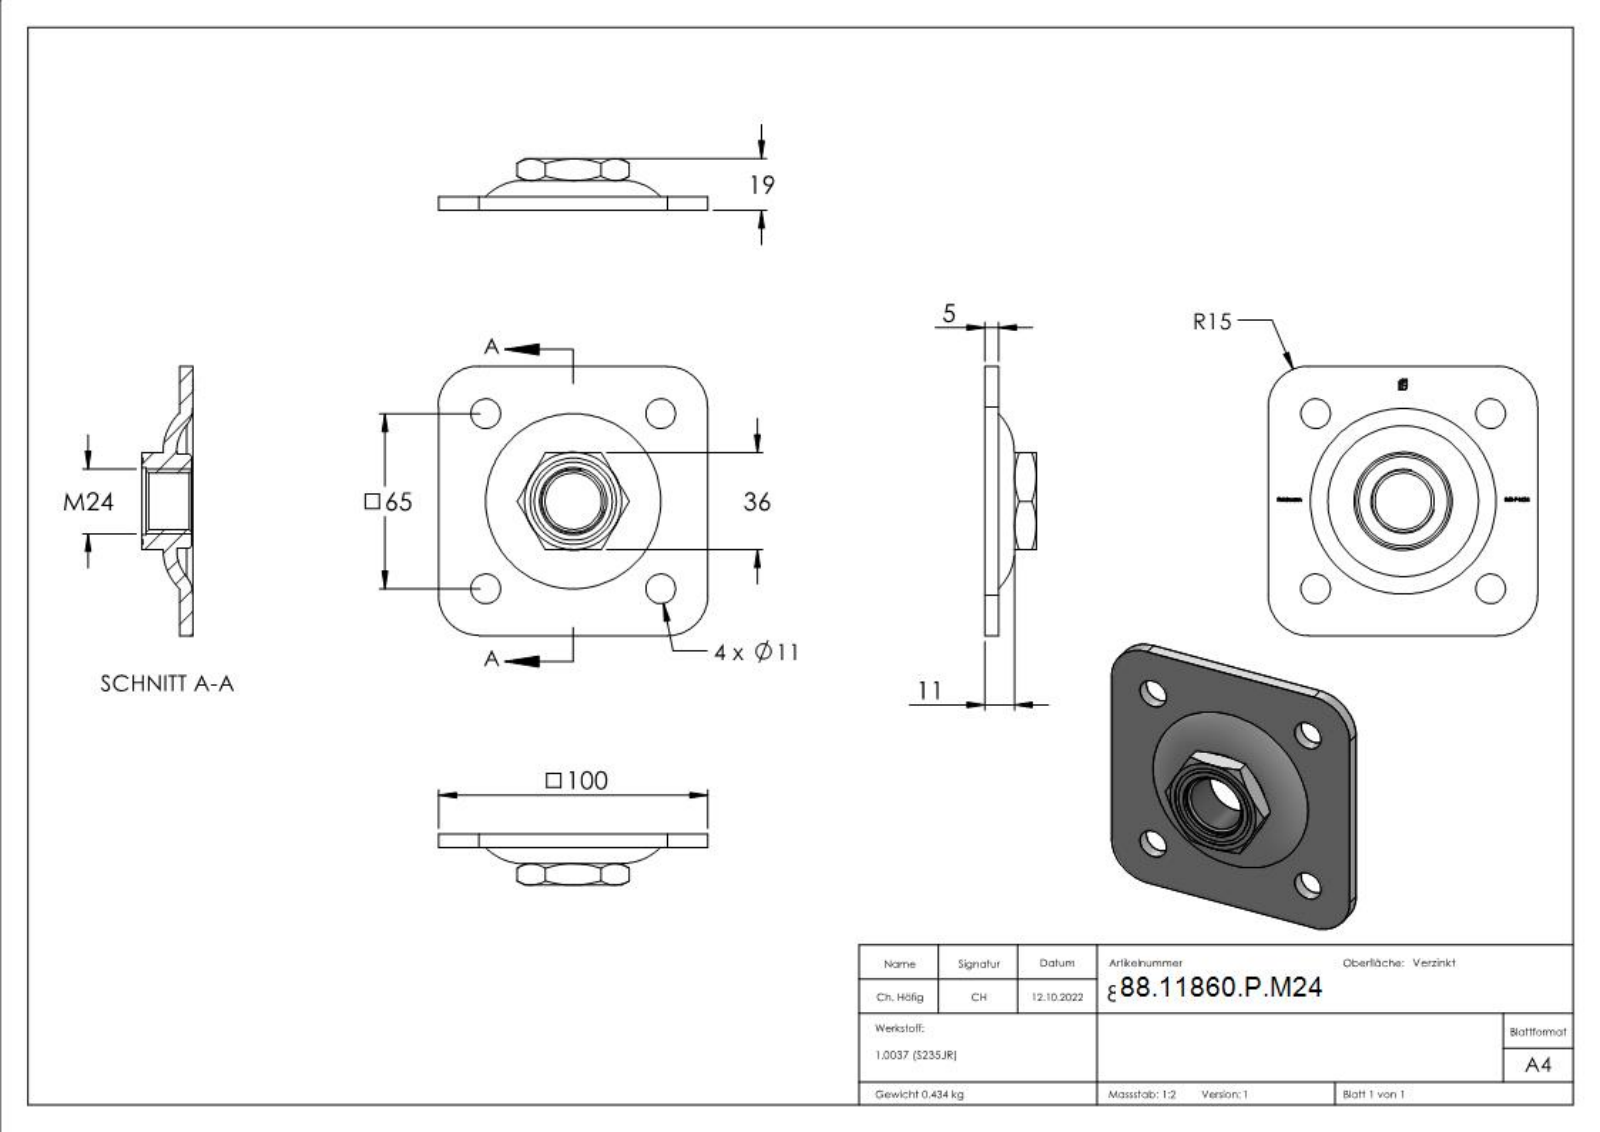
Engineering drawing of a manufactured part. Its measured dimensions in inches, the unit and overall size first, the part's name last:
Units: inches
Overall size (bounding box): 3.937 × 3.937 × 0.748
Round holes (diameter × count): ⌀0.433 ×4, ⌀0.827 ×1, ⌀0.984 ×1, ⌀1.26 ×1
Round bosses / shafts (diameter × count): ⌀1.378 ×1, ⌀1.142 ×1
Partial cylindrical surfaces — rounded edges, fillets, slot ends (radius × count): R0.591 ×4
Main face-to-face distances: 0.197, 3.937, 0.177, 0.02, 1.417, 0.748, 0.728, 0.551, 1.26, 2.677
Hole centre spacings: 1.809, 2.559, 3.619
Volume: 3.399 in³ · Surface area: 37.42 in²
Bodies: 1 solid, 319 faces (173 planar, 13 cylindrical, 133 other)
Part name (STEP PRODUCT): 860-P-M24
STEP written by: SolidWorks 2018 (CONFIG_CONTROL_DESIGN)
